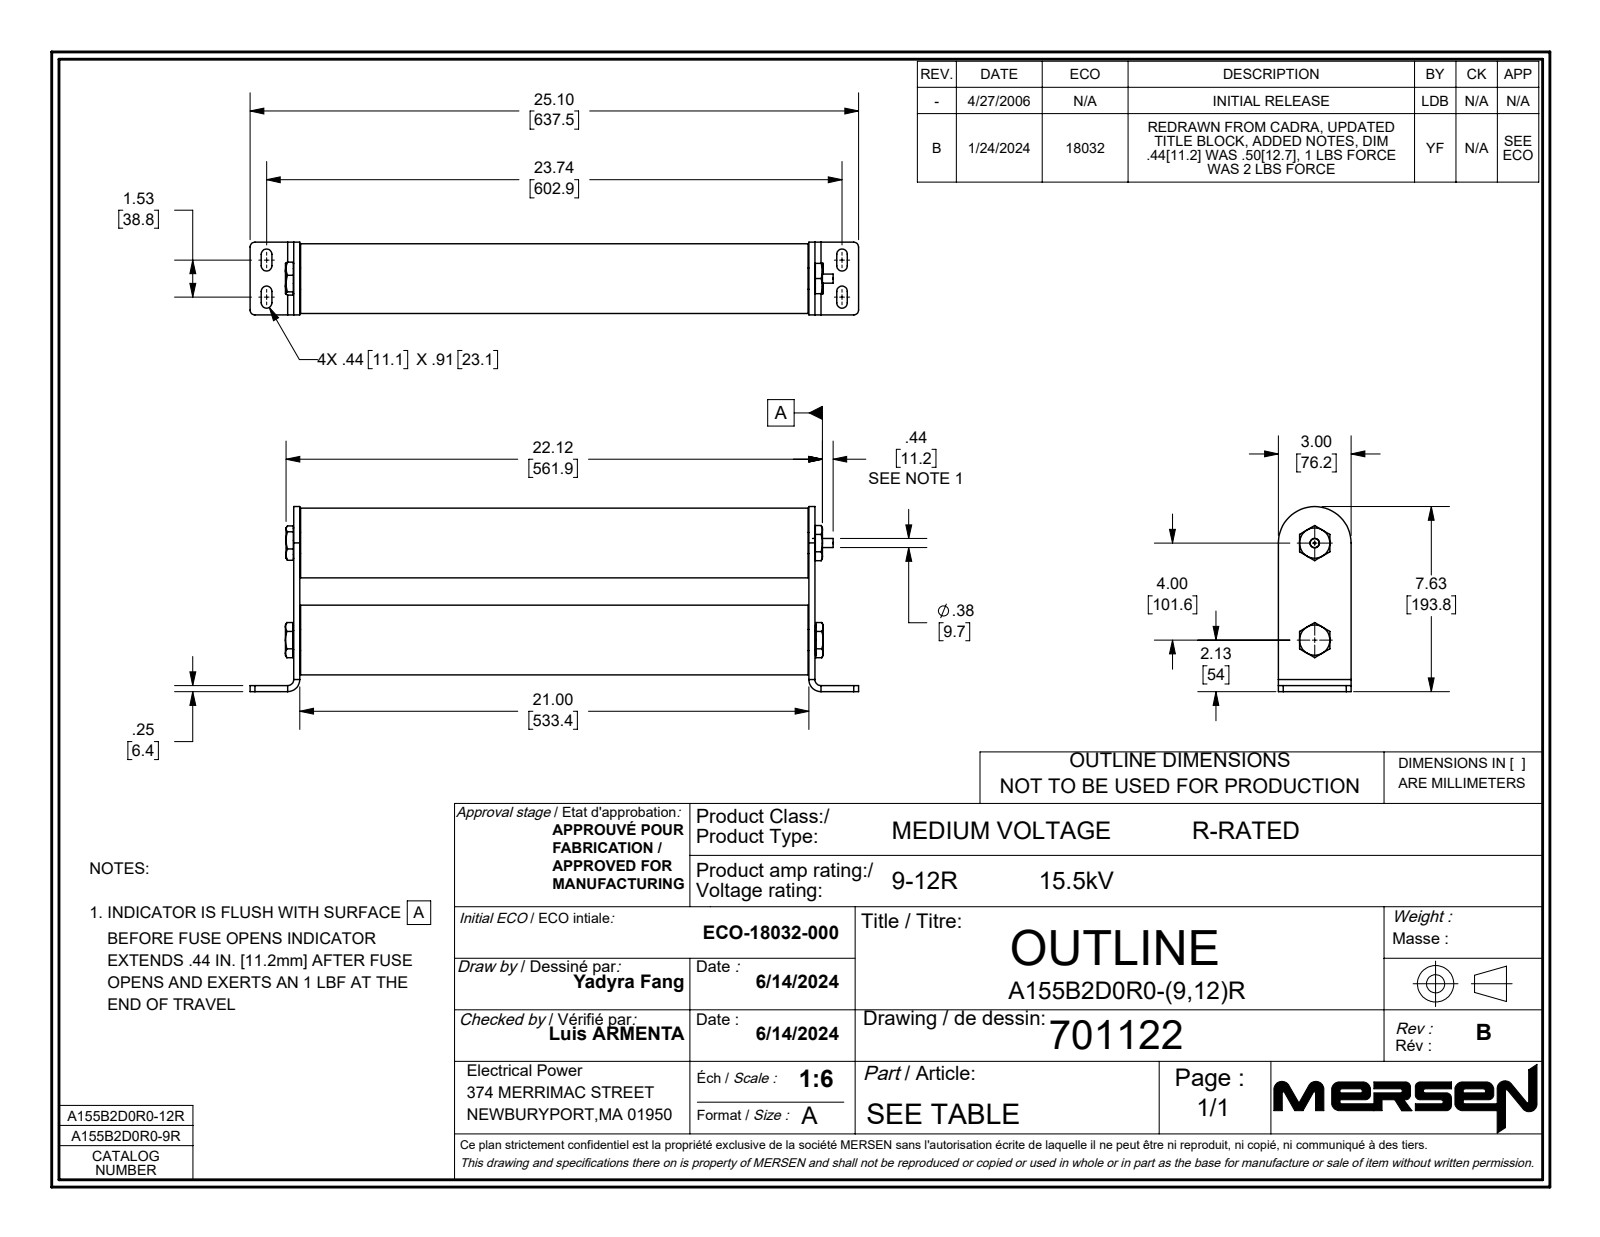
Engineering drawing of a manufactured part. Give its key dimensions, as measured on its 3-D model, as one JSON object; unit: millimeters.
{"part_name": "701122; 9399_9399", "step_written_by": "SolidWorks 2021 (AUTOMOTIVE_DESIGN)", "units": "millimeters", "bodies": {"solids": 11, "faces": 249, "planar": 101, "cylindrical": 88, "other": 60}, "overall_size": [637.5, 193.8, 76.2], "volume_mm3": 1004000, "surface_area_mm2": 563900, "round_holes": [[23, 2], [66.7, 2], [0.5, 1], [1.6, 1], [3.7, 1], [4.8, 1], [9.9, 1], [11.8, 1], [13, 1]], "round_bosses_or_shafts": [[73, 2], [31.8, 2], [22.2, 2], [19.9, 2], [22.2, 1], [19.8, 1], [14.3, 1], [11.5, 1]], "partial_cylinders_radius": [[5.6, 8], [5.1, 4], [6.4, 2], [12.7, 2], [38.1, 1]], "face_to_face_distances": [6.4, 539.8, 546.1, 533.4, 7.1, 539, 0.8, 532.6, 76.2, 31.8], "hole_center_spacings": [101.6]}
